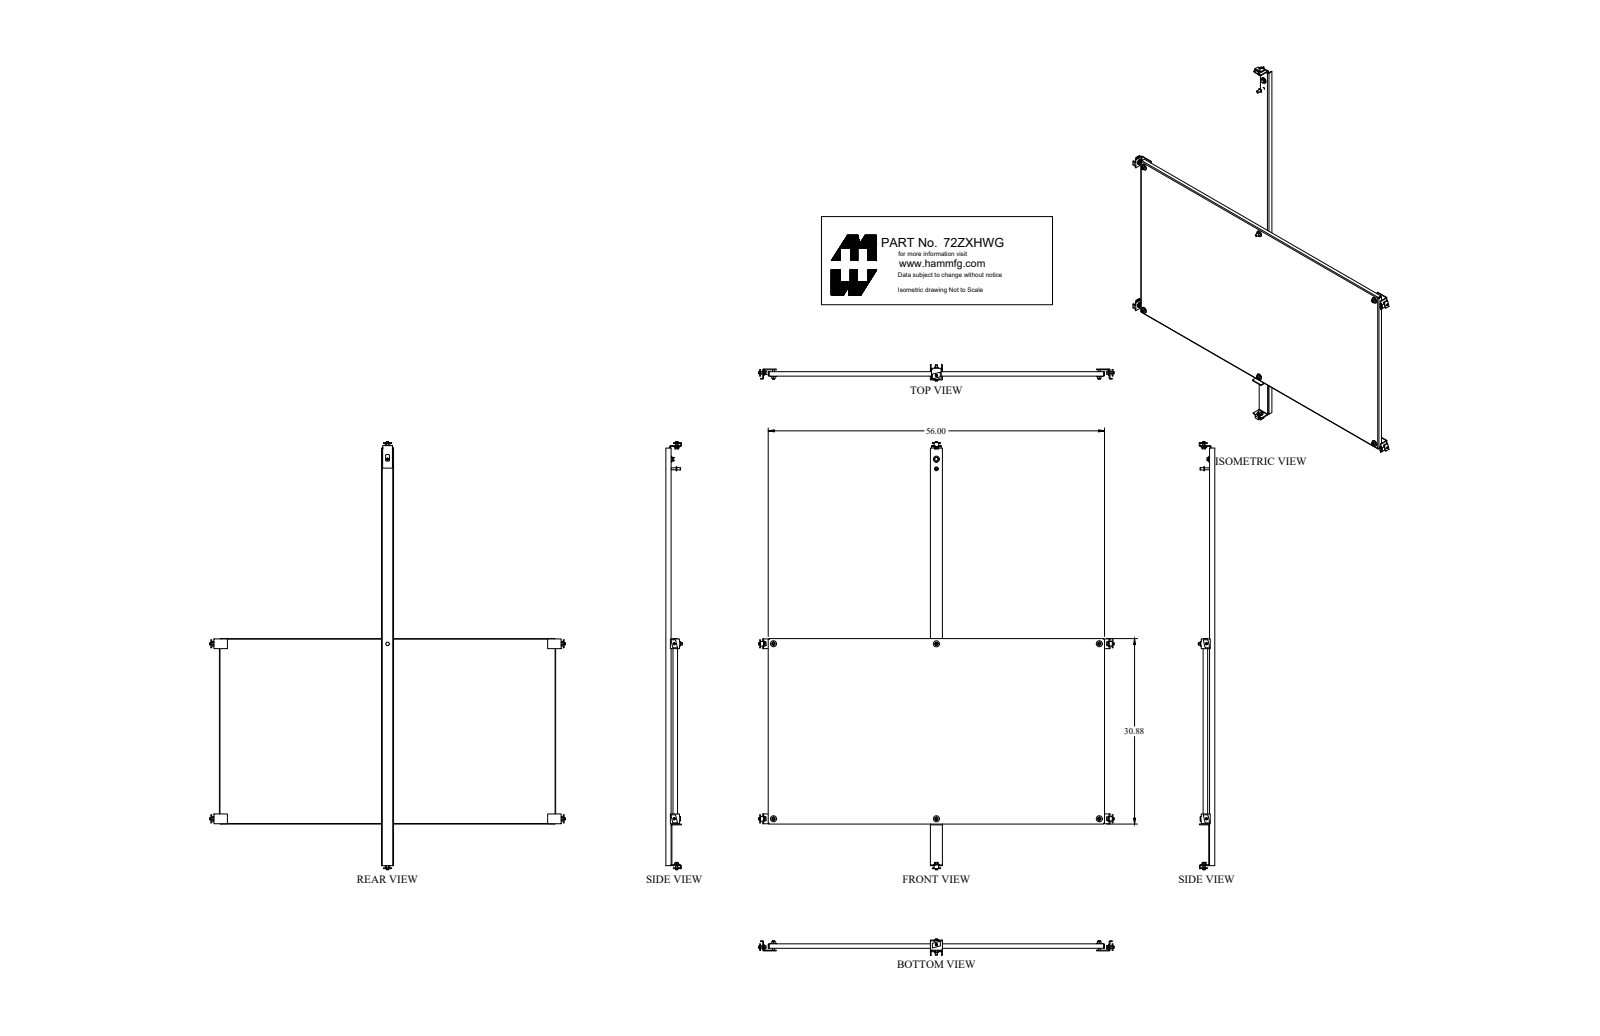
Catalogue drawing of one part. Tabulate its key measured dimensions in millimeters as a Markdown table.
| quantity | value |
| --- | --- |
| part name | 72ZXHWG_Default |
| STEP written by | SolidWorks 2018 (CONFIG_CONTROL_DESIGN) |
| units | millimeters |
| bodies | 14 solids, 305 faces (152 planar, 105 cylindrical, 48 other) |
| overall size | 1801 × 1488 × 65.9 |
| volume | 3 463 000 mm³ |
| surface area | 2 778 000 mm² |
| round holes (diameter × count) | 14.3 × 6, 11.1 × 5, 11.1 × 1, 11.5 × 1 |
| round bosses / shafts (diameter × count) | 16.5 × 6, 8.4 × 6, 9.5 × 4, 9.5 × 2 |
| partial cylindrical surfaces (radius × count) | 1.5 × 11, 4.7 × 11, 1.2 × 4, 3.6 × 4, 5.6 × 2 |
| main face-to-face distances | 2.4, 3.2, 30.1, 27, 24.6, 27.7, 3.2, 781.8, 50.8, 47.6 |
| hole center spacings | 1010.9, 739.8, 689, 689, 1378, 1564, 1669.2, 0.8 |
